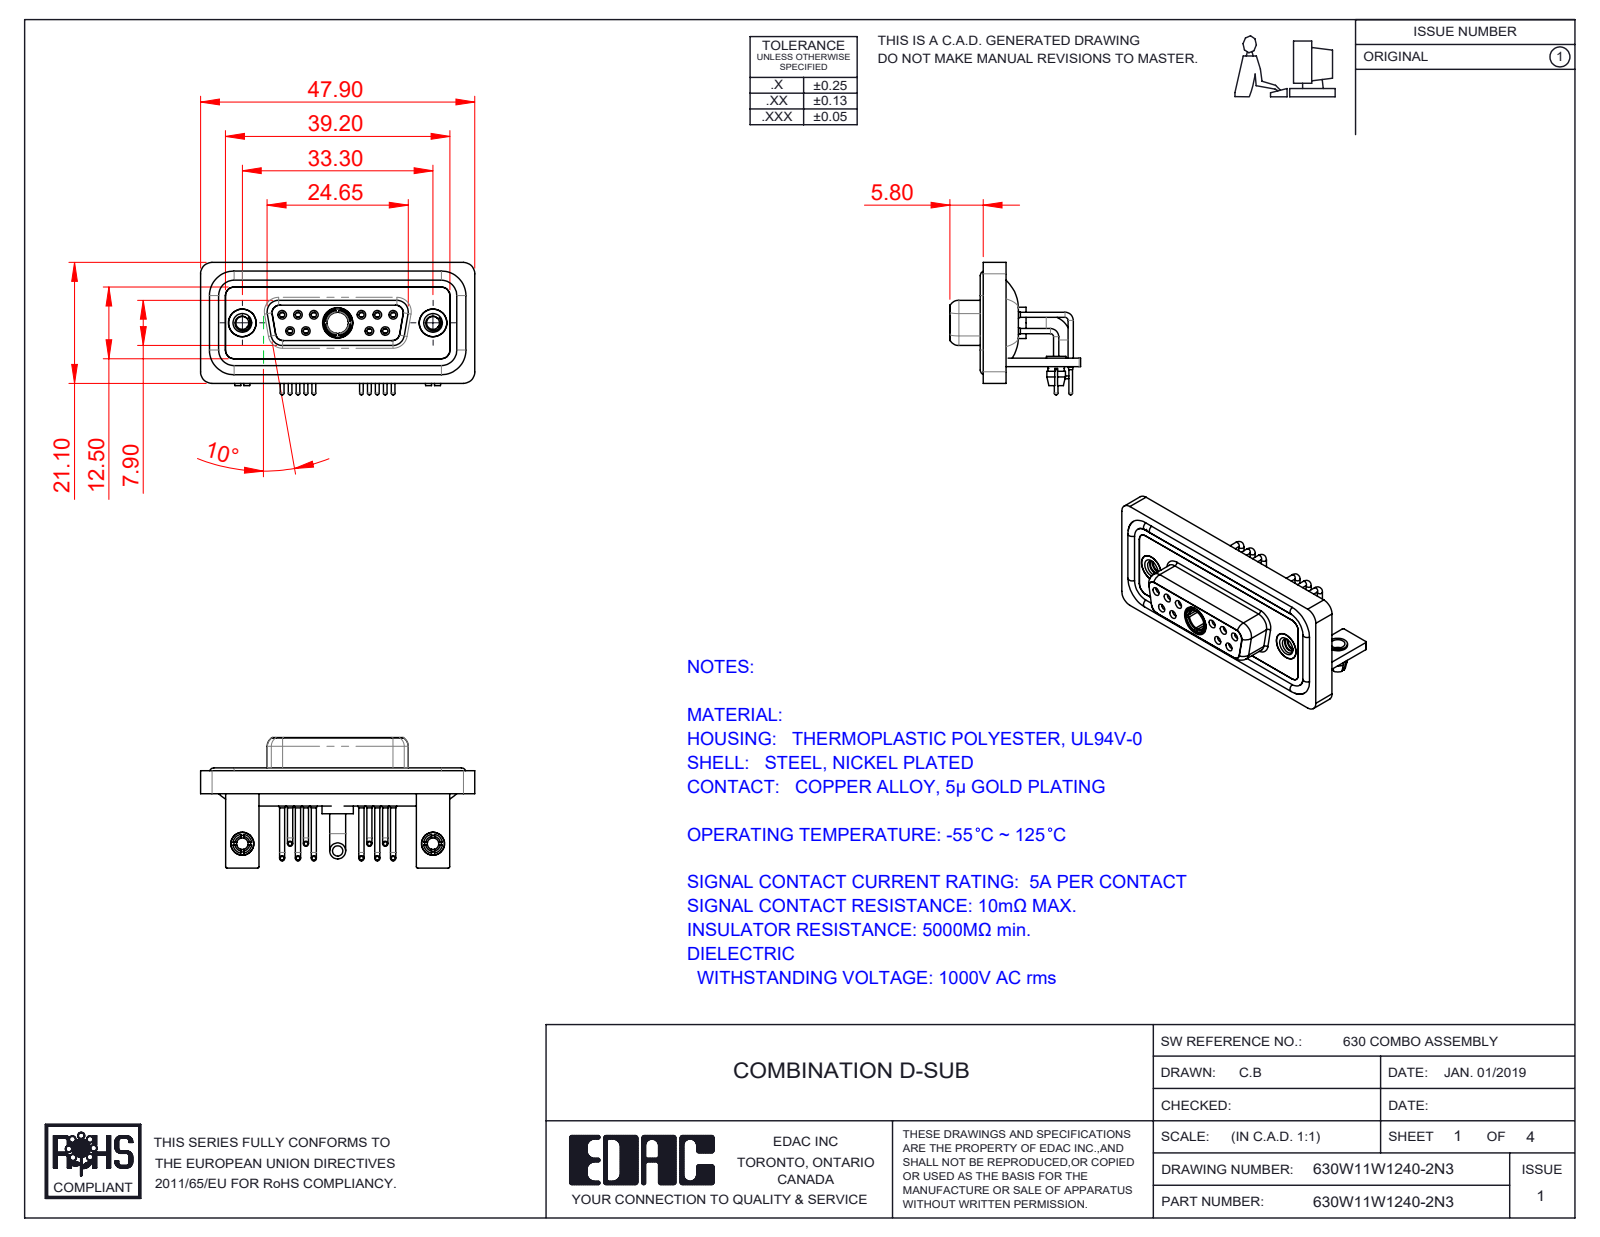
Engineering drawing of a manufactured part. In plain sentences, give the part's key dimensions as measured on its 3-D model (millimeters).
The part is named "630Combo Stabilizer Bracket_50 Contacts; 630W11W1240-2N3; 630Combo Shell Rear_15 Contacts; 630Combo Housing_11W1 (+7 more)". Its 3-D file was written by "SolidWorks 2020 (CONFIG_CONTROL_DESIGN)". It is 23 solids with 1134 faces: 352 planar, 499 cylindrical and 283 other. Overall it measures 47.9 by 23.12 by 22.8 millimeters. Its volume is 6 620 cubic millimeters and its surface area 11 417 square millimeters. Round holes: 12 of diameter 2, 10 of diameter 0.9, 10 of diameter 1.1, 10 of diameter 1.5, 6 of diameter 1.7, 4 of diameter 1.6, 3 of diameter 4.85, 2 of diameter 2.26, 2 of diameter 2.5, 2 of diameter 3.2, 2 of diameter 4, 2 of diameter 4.05. Round bosses or shafts: 10 of diameter 1.6, 10 of diameter 0.9, 10 of diameter 0.65, 2 of diameter 4.95, 2 of diameter 4.8, 2 of diameter 4, 2 of diameter 3.4, 2 of diameter 3.3. Partial cylindrical surfaces (rounded edges, fillets, slot ends): 21 of radius 2, 18 of radius 1.5, 16 of radius 0.25, 12 of radius 1.35, 8 of radius 1.6, 5 of radius 0.5, 4 of radius 0.6, 4 of radius 0.65. The main face-to-face distances are 0.4, 2.9, 1.5, 1.8, 3.7, 1.1, 1.6, 4.1, 0.8, 2.5. The hole center spacings are 3.16, 2.77, 13.85, 11.08, 16.62, 5.03, 5.04, 5.54.
